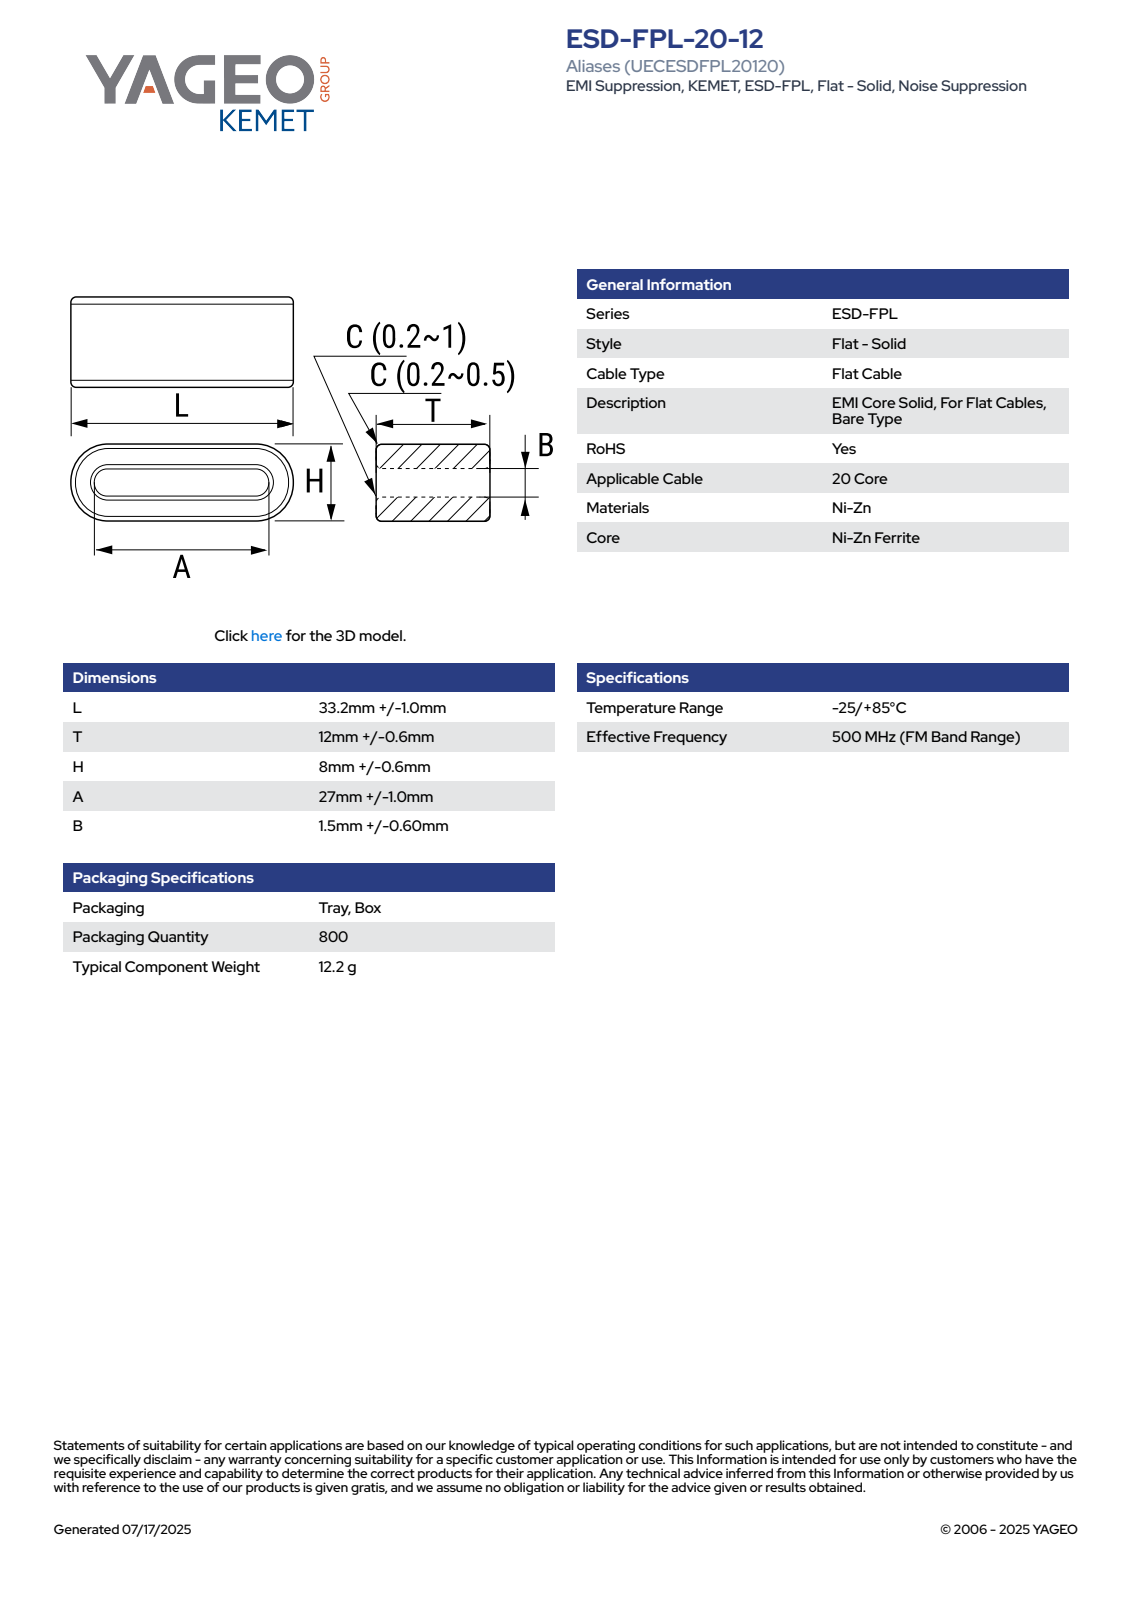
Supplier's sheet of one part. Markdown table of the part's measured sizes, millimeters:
| quantity | value |
| --- | --- |
| part name | EC_FPL3_L34.2T12.6H8.6A27B1.5 |
| STEP written by | SolidWorks 2021 (AUTOMOTIVE_DESIGN) |
| units | millimeters |
| bodies | 4 solids, 95 faces (63 planar, 16 cylindrical, 16 other) |
| overall size | 34.2 × 12.6 × 8.6 |
| volume | 2 999 mm³ |
| surface area | 2 165 mm² |
| partial cylindrical surfaces (radius × count) | 0.2 × 8, 0.75 × 2, 4.3 × 2 |
| main face-to-face distances | 3.55, 5.05, 8.6, 1.5, 12.6, 5.29, 7.31, 2.02, 5.68, 6.92 |
